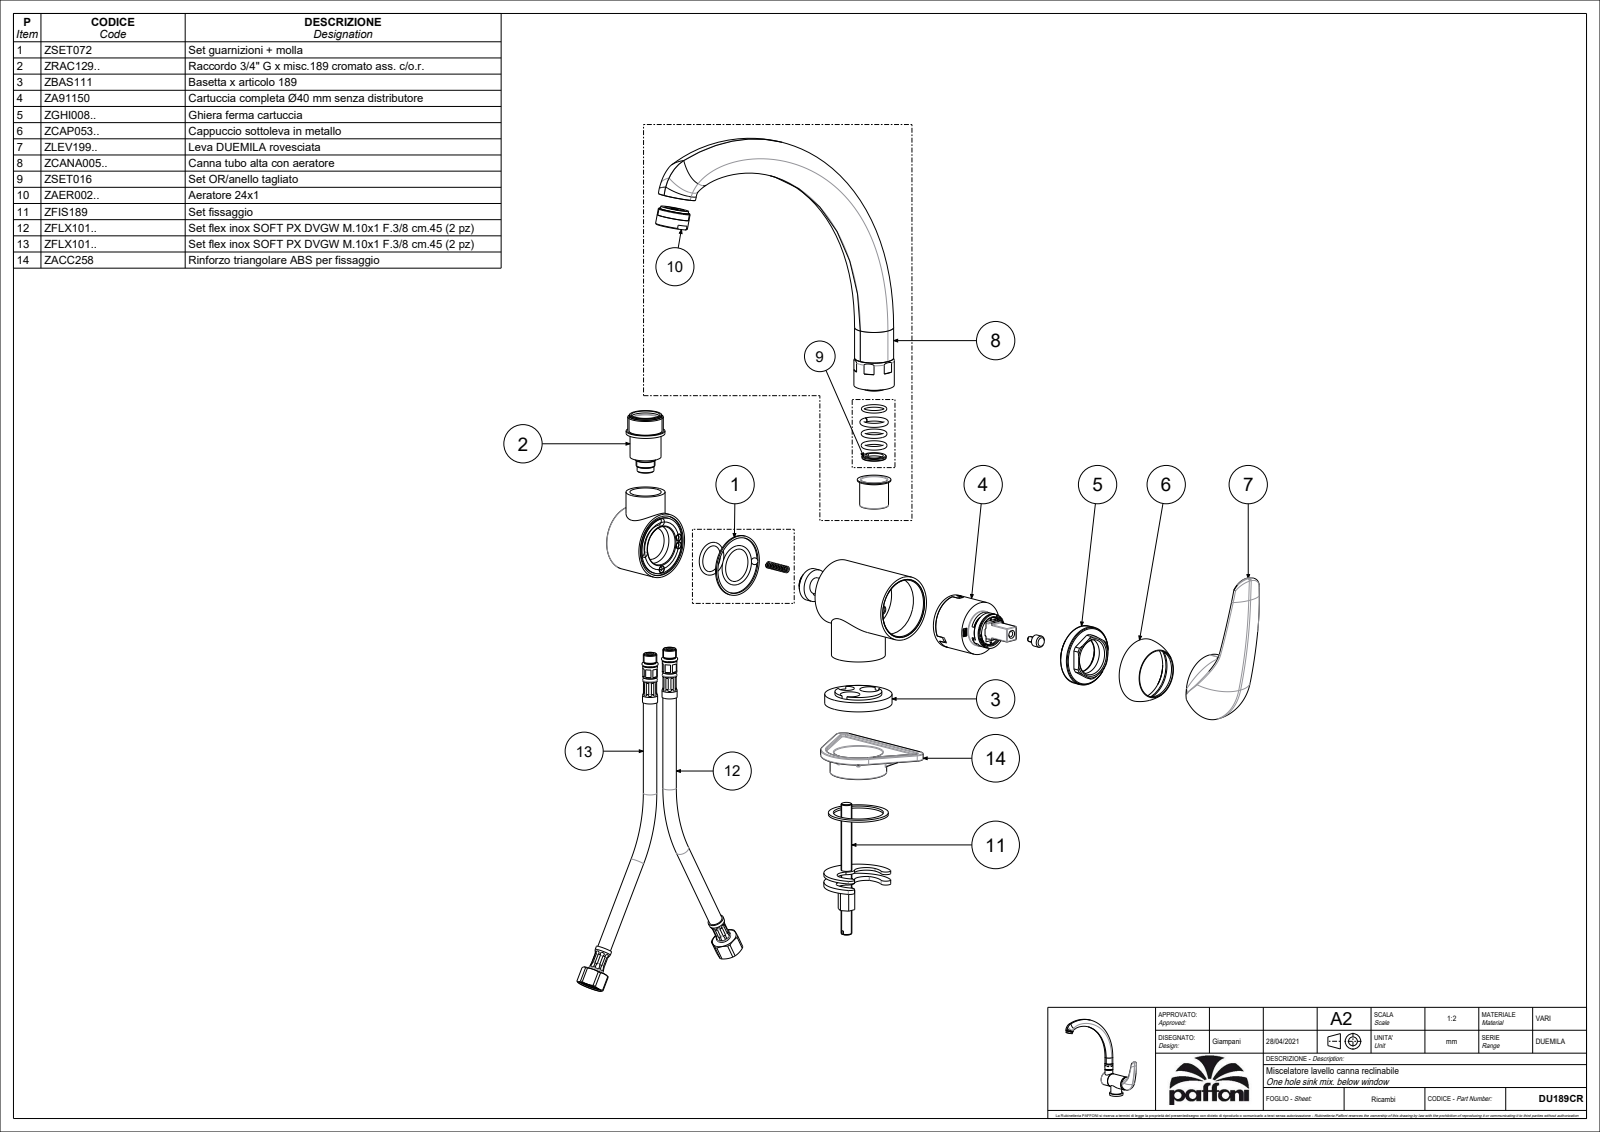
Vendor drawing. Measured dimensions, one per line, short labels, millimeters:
name: DU189CR
written by: CREO PARAMETRIC BY PTC INC, 2020044 (CONFIG_CONTROL_DESIGN)
unit: mm
bodies: 2 solids, 153 faces (41 planar, 46 cylindrical, 66 other)
size: 308.29 × 245.52 × 153.52
volume: 519 294 mm³; area: 76 543 mm²
holes: 1× ⌀9.2, 1× ⌀18.2, 1× ⌀18.5, 1× ⌀21.2, 1× ⌀27
bosses: 2× ⌀24, 1× ⌀50, 1× ⌀48, 1× ⌀40, 1× ⌀30, 1× ⌀29, 1× ⌀28.8, 1× ⌀26.4
rounds: 2× R1.5, 2× R15, 2× R24, 2× R24.5, 1× R18, 1× R39.04, 1× R340.59, 1× R341.58
face distances: 7, 113.29, 106.29, 0.5, 112.79, 105.79, 92.53, 85.53, 20.26, 20.76
hole spacings: 106.2
